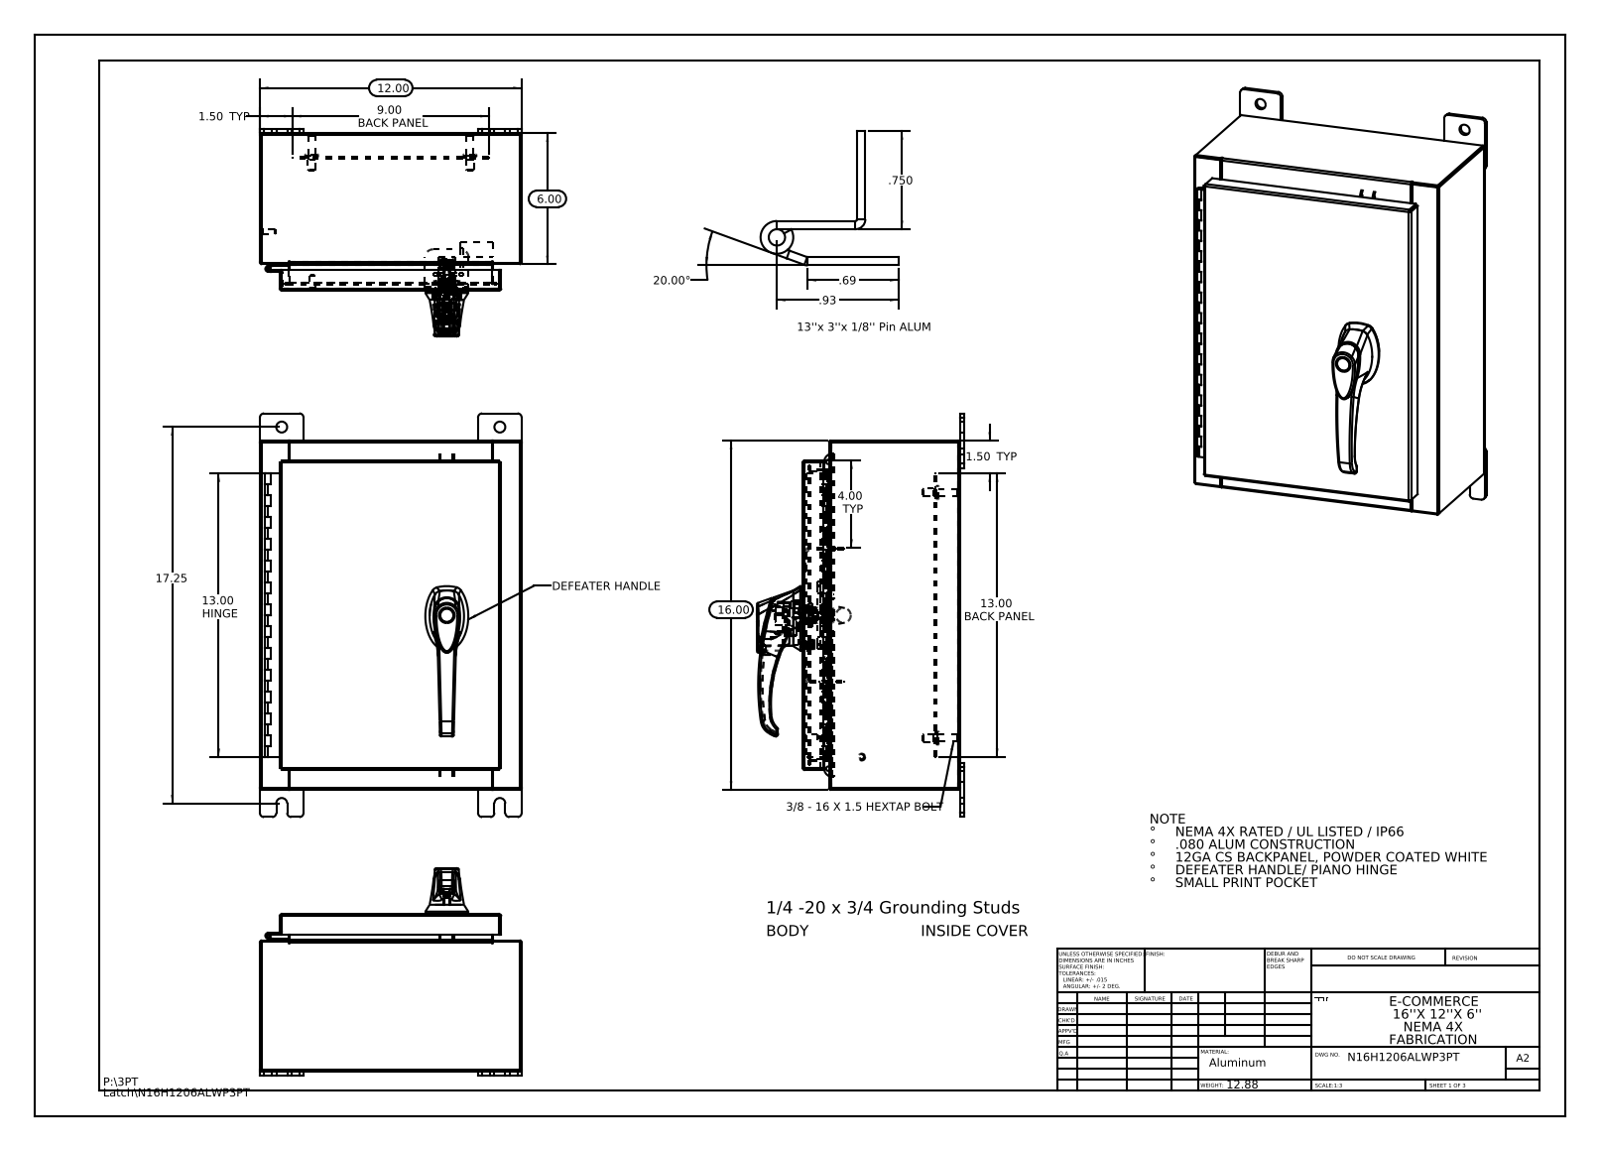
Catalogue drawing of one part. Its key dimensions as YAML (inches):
part_name: "NMP-SS-RODGUIDES; Quarter-20 CD Stud; 00005309_G26103101; N16H1206ALWP3PT Backpanel (+8 more)"
step_written_by: "SolidWorks 2013 (CONFIG_CONTROL_DESIGN)"
units: inches
bodies: {solids: 37, faces: 2290, planar: 775, cylindrical: 817, other: 698}
overall_size: [18.5, 12, 9.495]
volume: 88.96
surface_area: 2171
round_holes:
  - {diameter: 0.5, count: 8}
  - {diameter: 0.25, count: 4}
  - {diameter: 0.138, count: 3}
  - {diameter: 0.161, count: 3}
  - {diameter: 0.079, count: 2}
  - {diameter: 0.203, count: 2}
  - {diameter: 0.313, count: 2}
  - {diameter: 0.437, count: 2}
  - {diameter: 0.125, count: 1}
  - {diameter: 0.125, count: 1}
  - {diameter: 0.197, count: 1}
  - {diameter: 0.276, count: 1}
round_bosses_or_shafts:
  - {diameter: 0.625, count: 4}
  - {diameter: 0.375, count: 4}
  - {diameter: 0.33, count: 4}
  - {diameter: 0.157, count: 4}
  - {diameter: 0.14, count: 4}
  - {diameter: 0.315, count: 3}
  - {diameter: 0.236, count: 3}
  - {diameter: 1.181, count: 1}
partial_cylinders:
  - {radius: 0.118, count: 37}
  - {radius: 0.006, count: 33}
  - {radius: 0.19, count: 24}
  - {radius: 0.013, count: 20}
  - {radius: 0.088, count: 18}
  - {radius: 0.039, count: 15}
  - {radius: 0.028, count: 12}
  - {radius: 0.008, count: 6}
face_to_face_distances: [0.075, 7.126, 11.925, 7.051, 7.201, 15.925, 5.925, 1.201, 1, 0.104]
hole_center_spacings: [3.708, 0.295, 0.625, 0.841, 1.25, 1.313, 1.32, 1.484]
